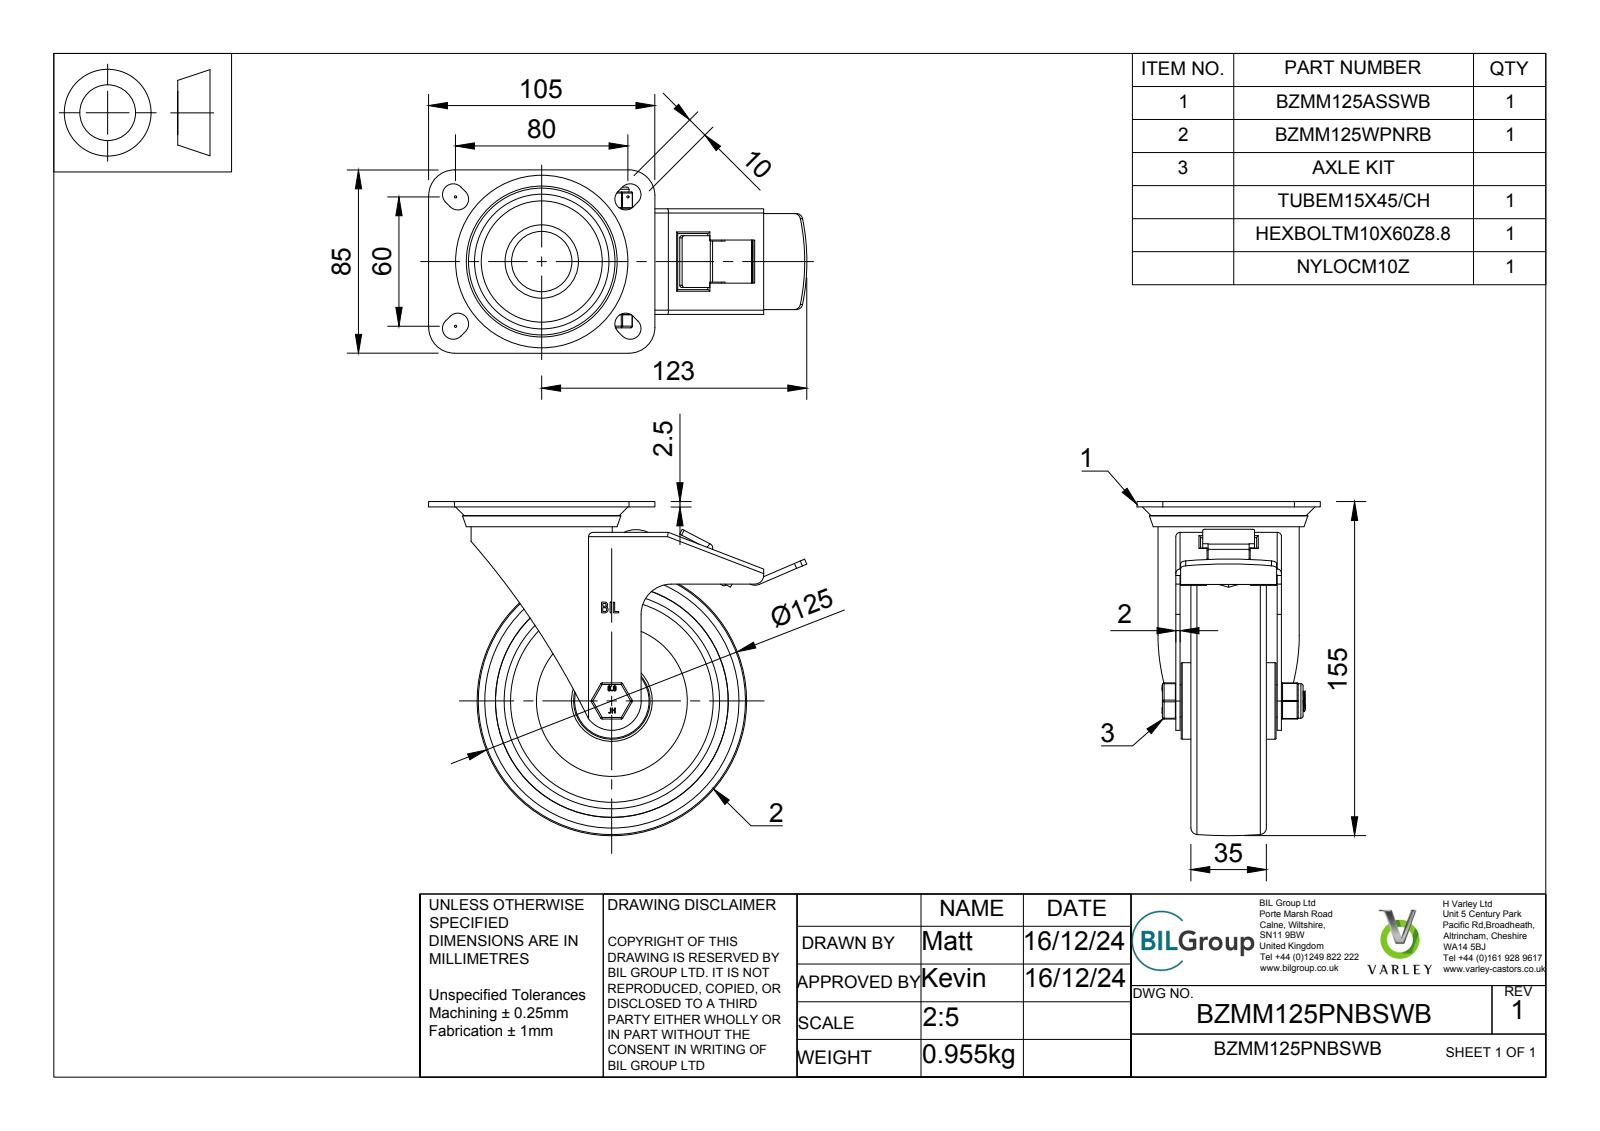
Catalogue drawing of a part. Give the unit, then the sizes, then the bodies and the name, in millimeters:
Units: millimetres
Overall size (bounding box): 175.5 × 155 × 85
Round holes (diameter × count): ⌀6 ×2, ⌀10 ×1, ⌀10.2 ×1, ⌀12 ×1, ⌀15.5 ×1, ⌀16 ×1, ⌀23.5 ×1, ⌀26 ×1, ⌀28 ×1, ⌀40 ×1, ⌀61.5 ×1, ⌀100 ×1
Round bosses / shafts (diameter × count): ⌀4 ×8, ⌀65.5 ×1, ⌀35.5 ×1, ⌀34 ×1, ⌀25.9 ×1, ⌀22.75 ×1, ⌀14.95 ×1, ⌀9.85 ×1
Partial cylindrical surfaces — rounded edges, fillets, slot ends (radius × count): R0.5 ×18, R0.75 ×16, R1.5 ×12, R5 ×9, R1 ×8, R2 ×6, R3 ×4, R12 ×4
Main face-to-face distances: 5, 2, 7, 19.75, 20.25, 40, 15.25, 22.25, 26.75, 42
Hole centre spacings: 43.75
Volume: 319 766 mm³ · Surface area: 169 738 mm²
Bodies: 24 solids, 721 faces (387 planar, 233 cylindrical, 101 other)
Part name (STEP PRODUCT): BZMM125PNBSWB v3; BZMM125ASSWB v1; ZINC PLATED, PRESSED STEEL TOP PLATE; ZINC PLATED, PRESSED STEEL FORKS (+8 more)
STEP written by: Autodesk Translation Framework v13.20.0.188 (AP242_MANAGED_MODEL_BASED_3D_ENGINEERING_MIM_LF)
